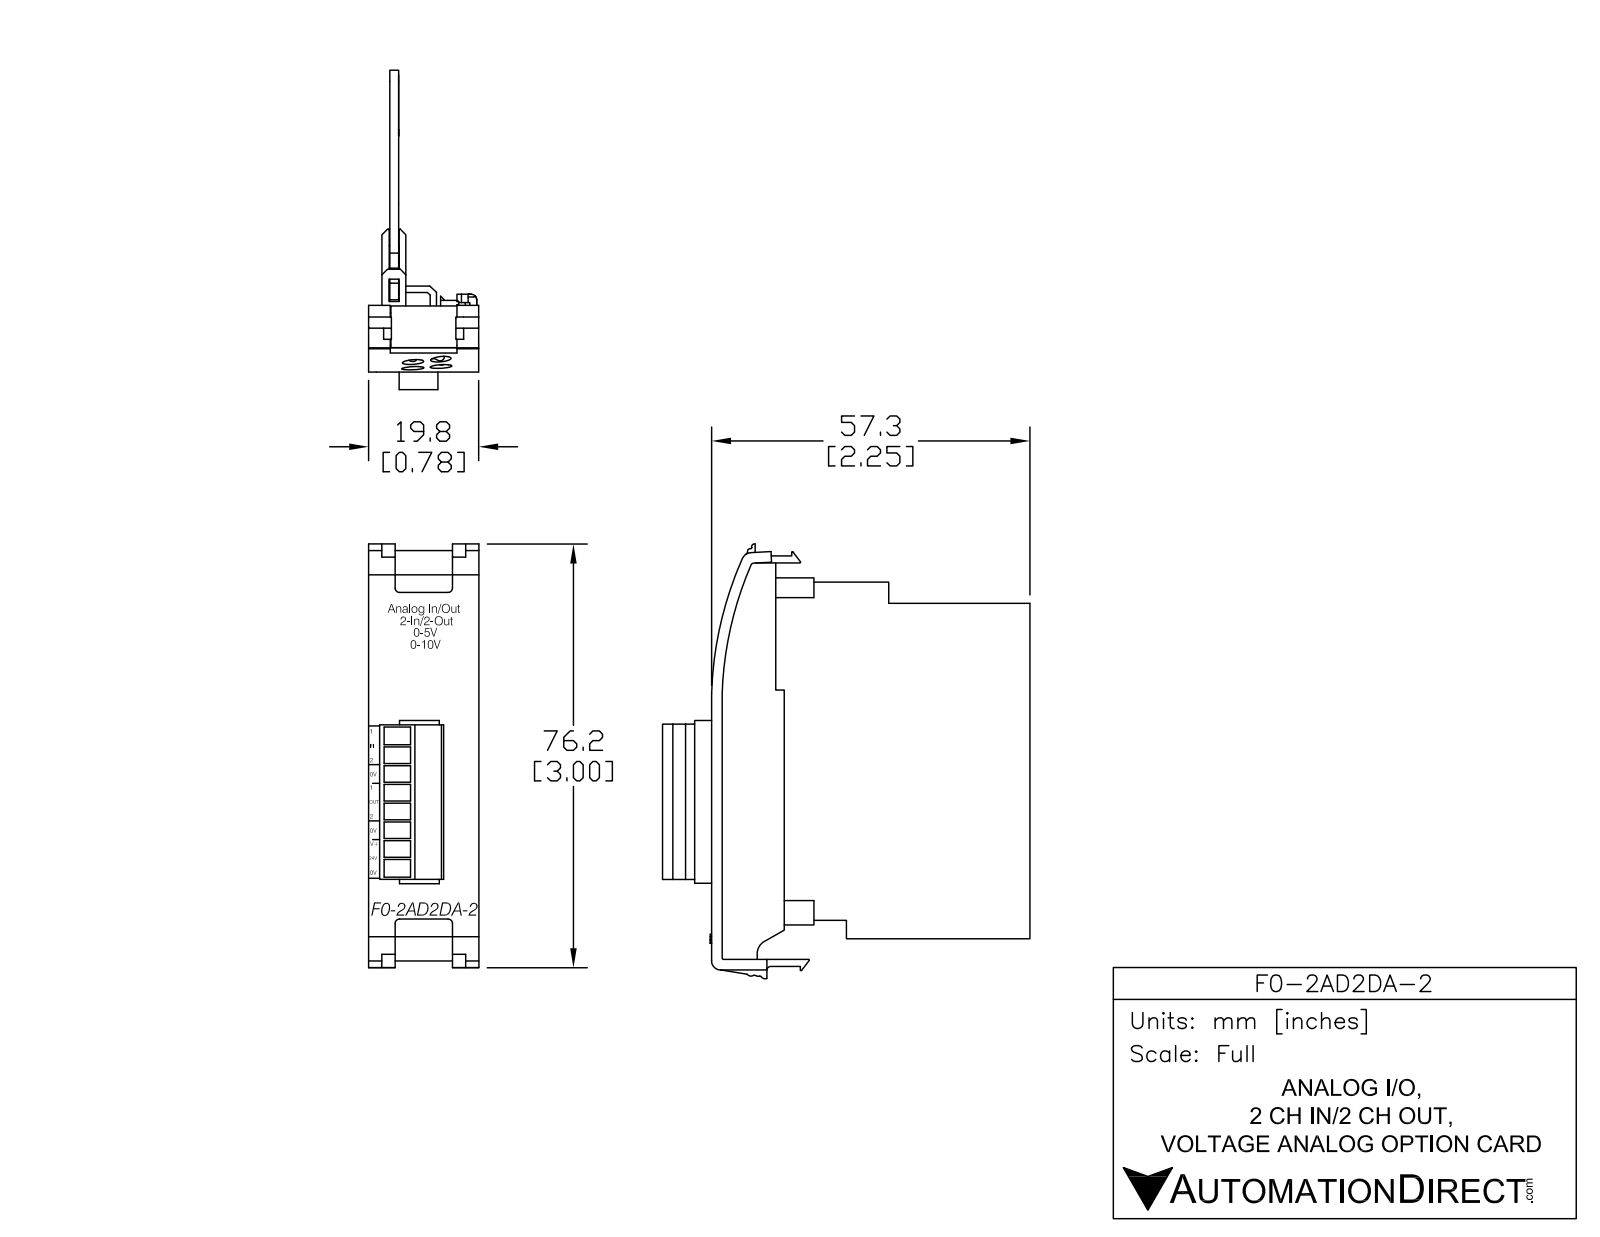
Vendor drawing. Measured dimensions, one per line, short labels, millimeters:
name: F0-2AD2DA-2
written by: SolidWorks 2009 (AUTOMOTIVE_DESIGN)
unit: mm
bodies: 2 solids, 342 faces (266 planar, 35 cylindrical, 41 other)
size: 78.2 × 66.1 × 21
volume: 12 000 mm³; area: 14 710 mm²
rounds: 4× R0.1, 3× R0.5, 3× R0.9, 2× R0.6, 1× R0.3, 1× R1.7, 1× R1.8, 1× R2.5
face distances: 1.6, 16, 1.3, 1.9, 2.9, 14.8, 13.2, 17.3, 14.5, 5
